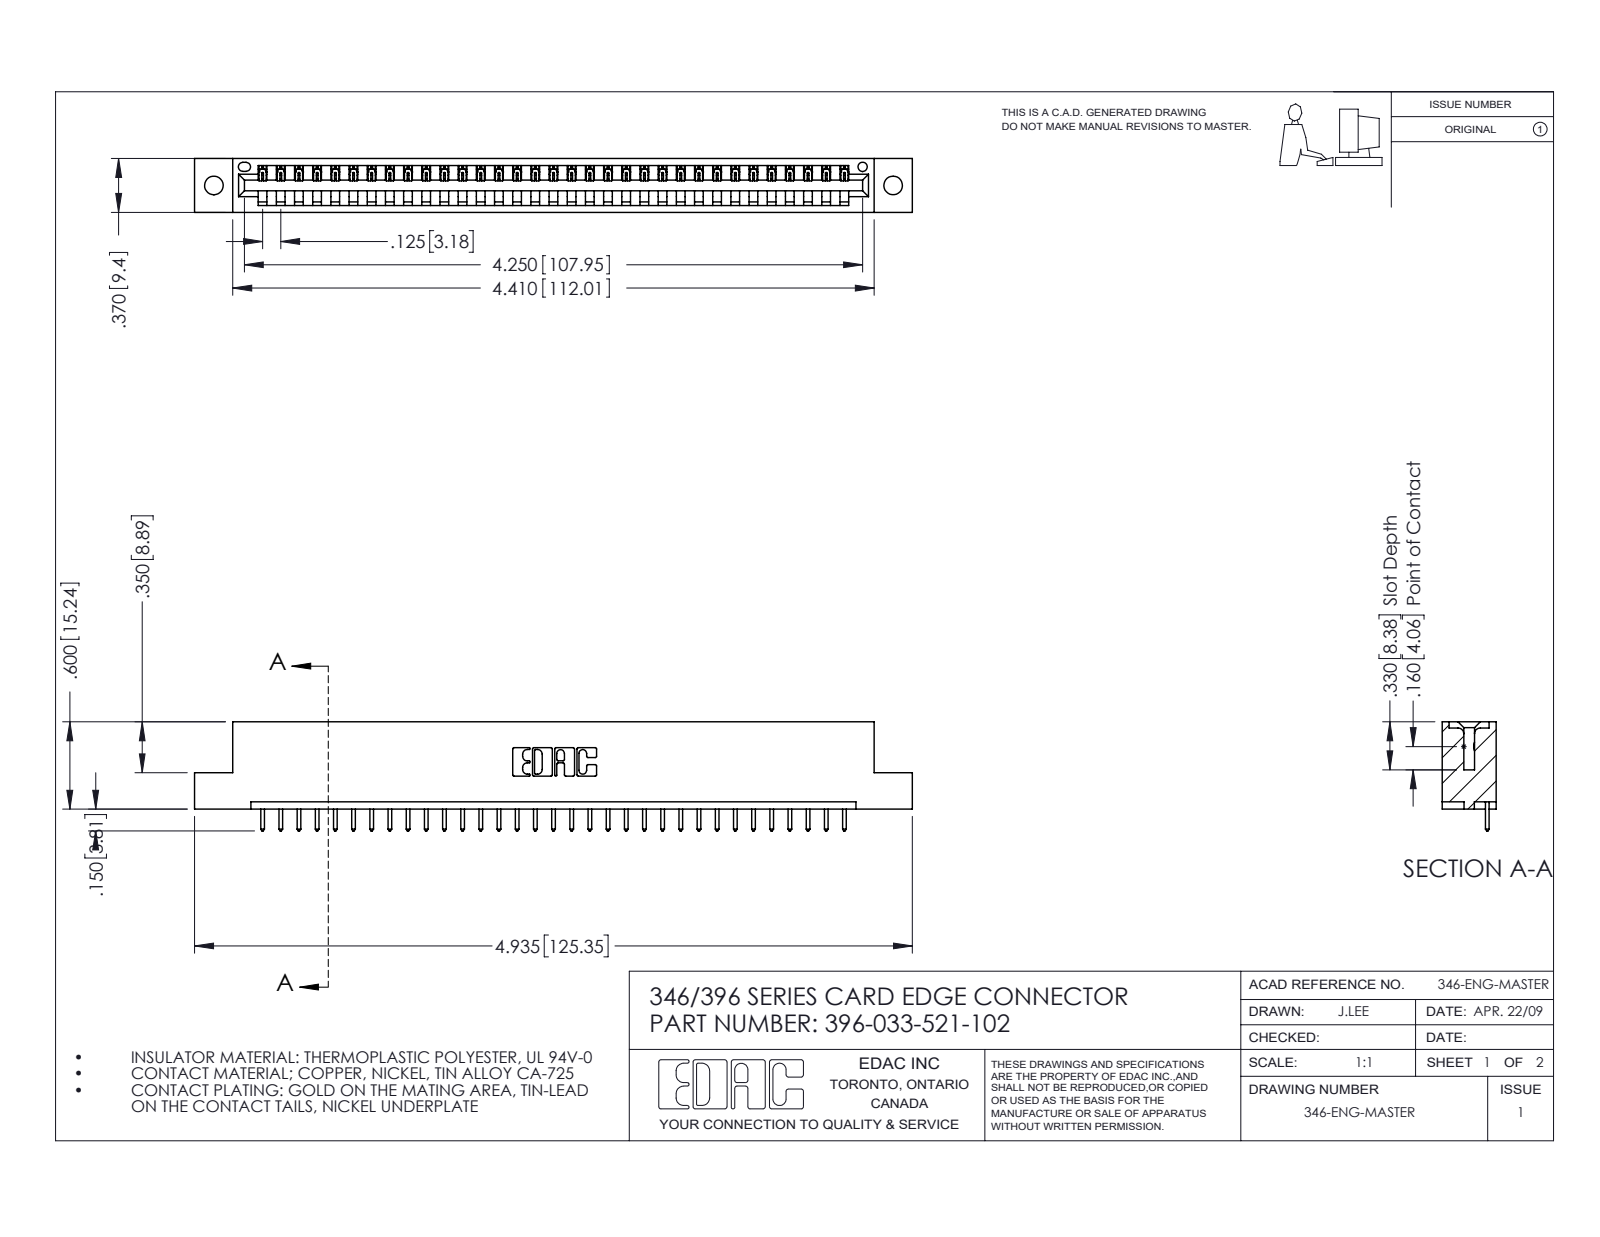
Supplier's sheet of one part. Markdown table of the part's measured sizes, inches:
| quantity | value |
| --- | --- |
| part name | 346 Part_Flush Mounting Lugs - 0.128 Dia; 396-033-521-102; 345-292-001_345-293-121 |
| STEP written by | SolidWorks 2016 (CONFIG_CONTROL_DESIGN) |
| units | inches |
| bodies | 34 solids, 2036 faces (1396 planar, 640 cylindrical, 0 other) |
| overall size | 4.935 × 0.75 × 0.37 |
| volume | 0.72 in³ |
| surface area | 21.72 in² |
| round holes (diameter × count) | 0.128 × 2, 0.064 × 1 |
| partial cylindrical surfaces (radius × count) | 0.006 × 66, 0.01 × 66, 0.01 × 22, 0.007 × 6, 0.031 × 6, 0.026 × 3, 0.031 × 2, 0.04 × 2 |
| main face-to-face distances | 0.048, 0.322, 0.37, 0.25, 0.072, 0.298, 0.025, 0.148, 0.222, 0.1 |
| hole center spacings | 0.246, 4.462, 4.67 |
